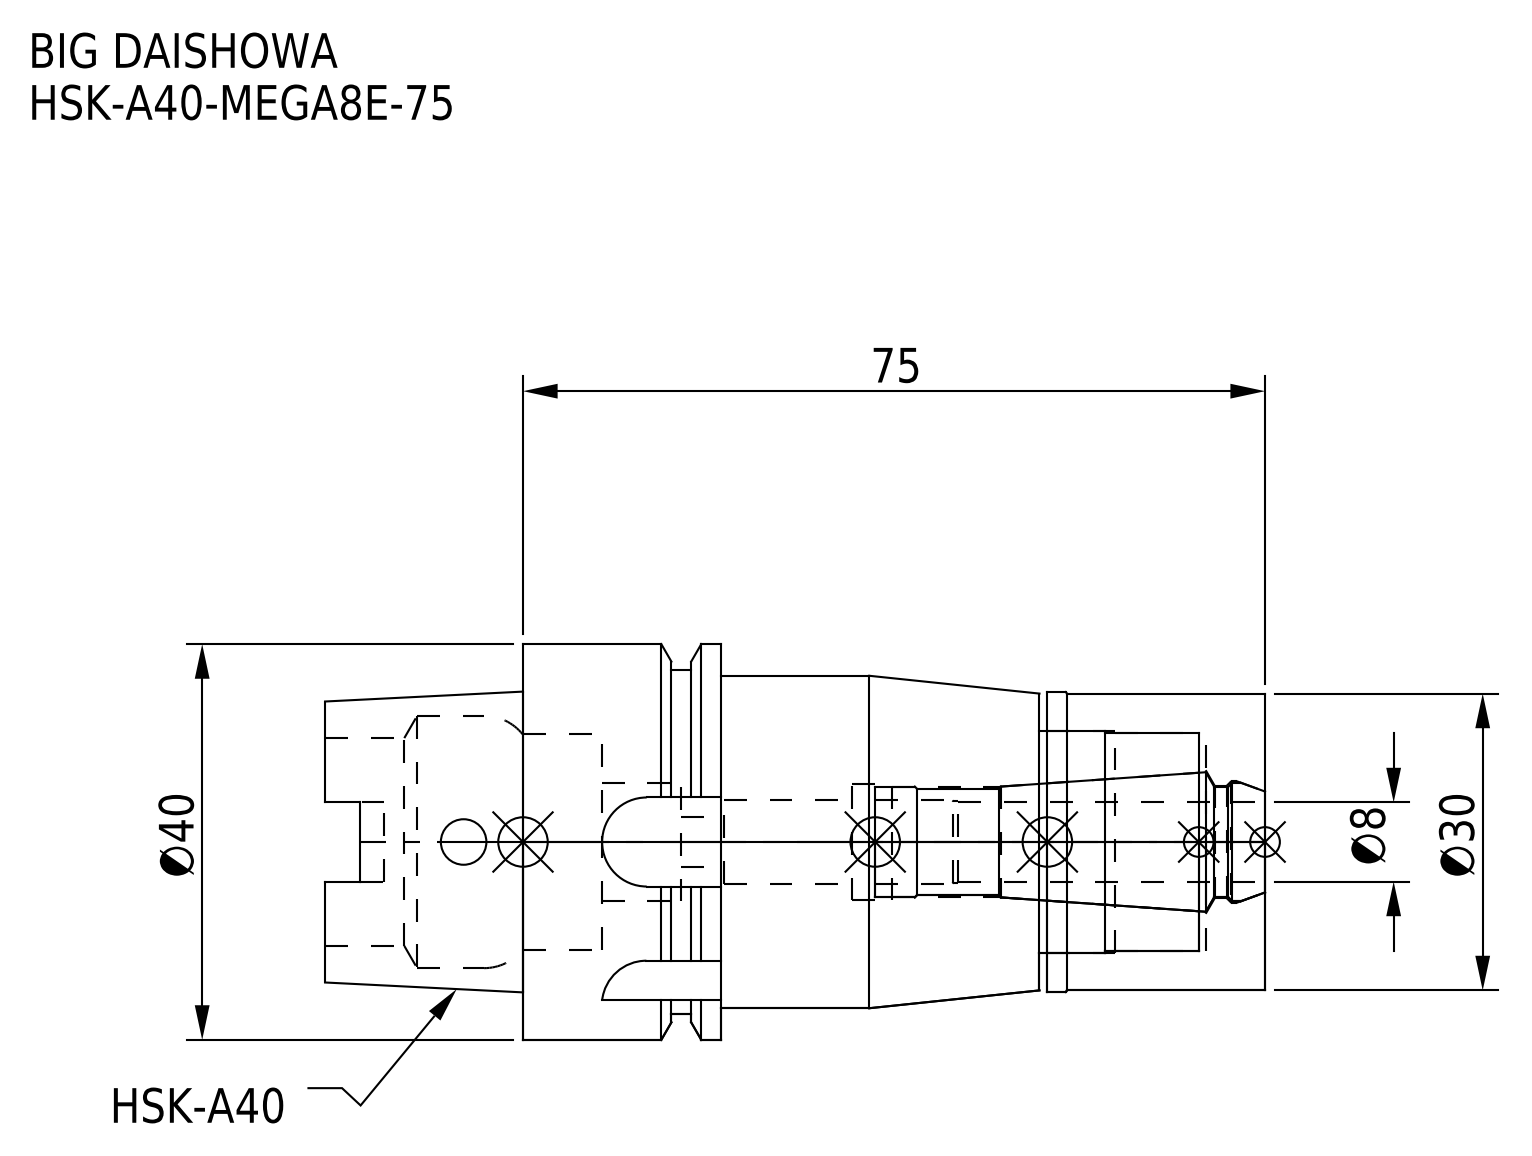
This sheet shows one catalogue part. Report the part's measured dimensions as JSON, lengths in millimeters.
{"part_name": "HSK-A40-MEGA8E-75_1.stp; HSK-A40-MEGA8E-75; DXF_TEMP_ASSY_ASM_4_ASM.stp; HSK-A40-MEGA8E-75-080-FreeParts (+3 more)", "step_written_by": "SolidWorks 2019 (CONFIG_CONTROL_DESIGN)", "units": "millimeters", "bodies": {"solids": 2, "faces": 127, "planar": 45, "cylindrical": 56, "other": 26}, "overall_size": [95, 40, 40], "volume_mm3": 61552, "surface_area_mm2": 20082, "round_holes": [[4.6, 1], [5, 1], [8.4, 1], [11.2, 1], [11.4, 1], [11.8, 1], [12, 1], [12.3, 1], [21, 1], [21.8, 1], [22, 1], [22.5, 1]], "round_bosses_or_shafts": [[40, 1], [34.8, 1], [33.6, 1], [30.3, 1], [30, 1]], "partial_cylinders_radius": [[1.88, 4], [4.5, 4]], "face_to_face_distances": [75, 20, 22, 53, 22.8, 0.8, 52.2, 55, 33, 32.2]}
